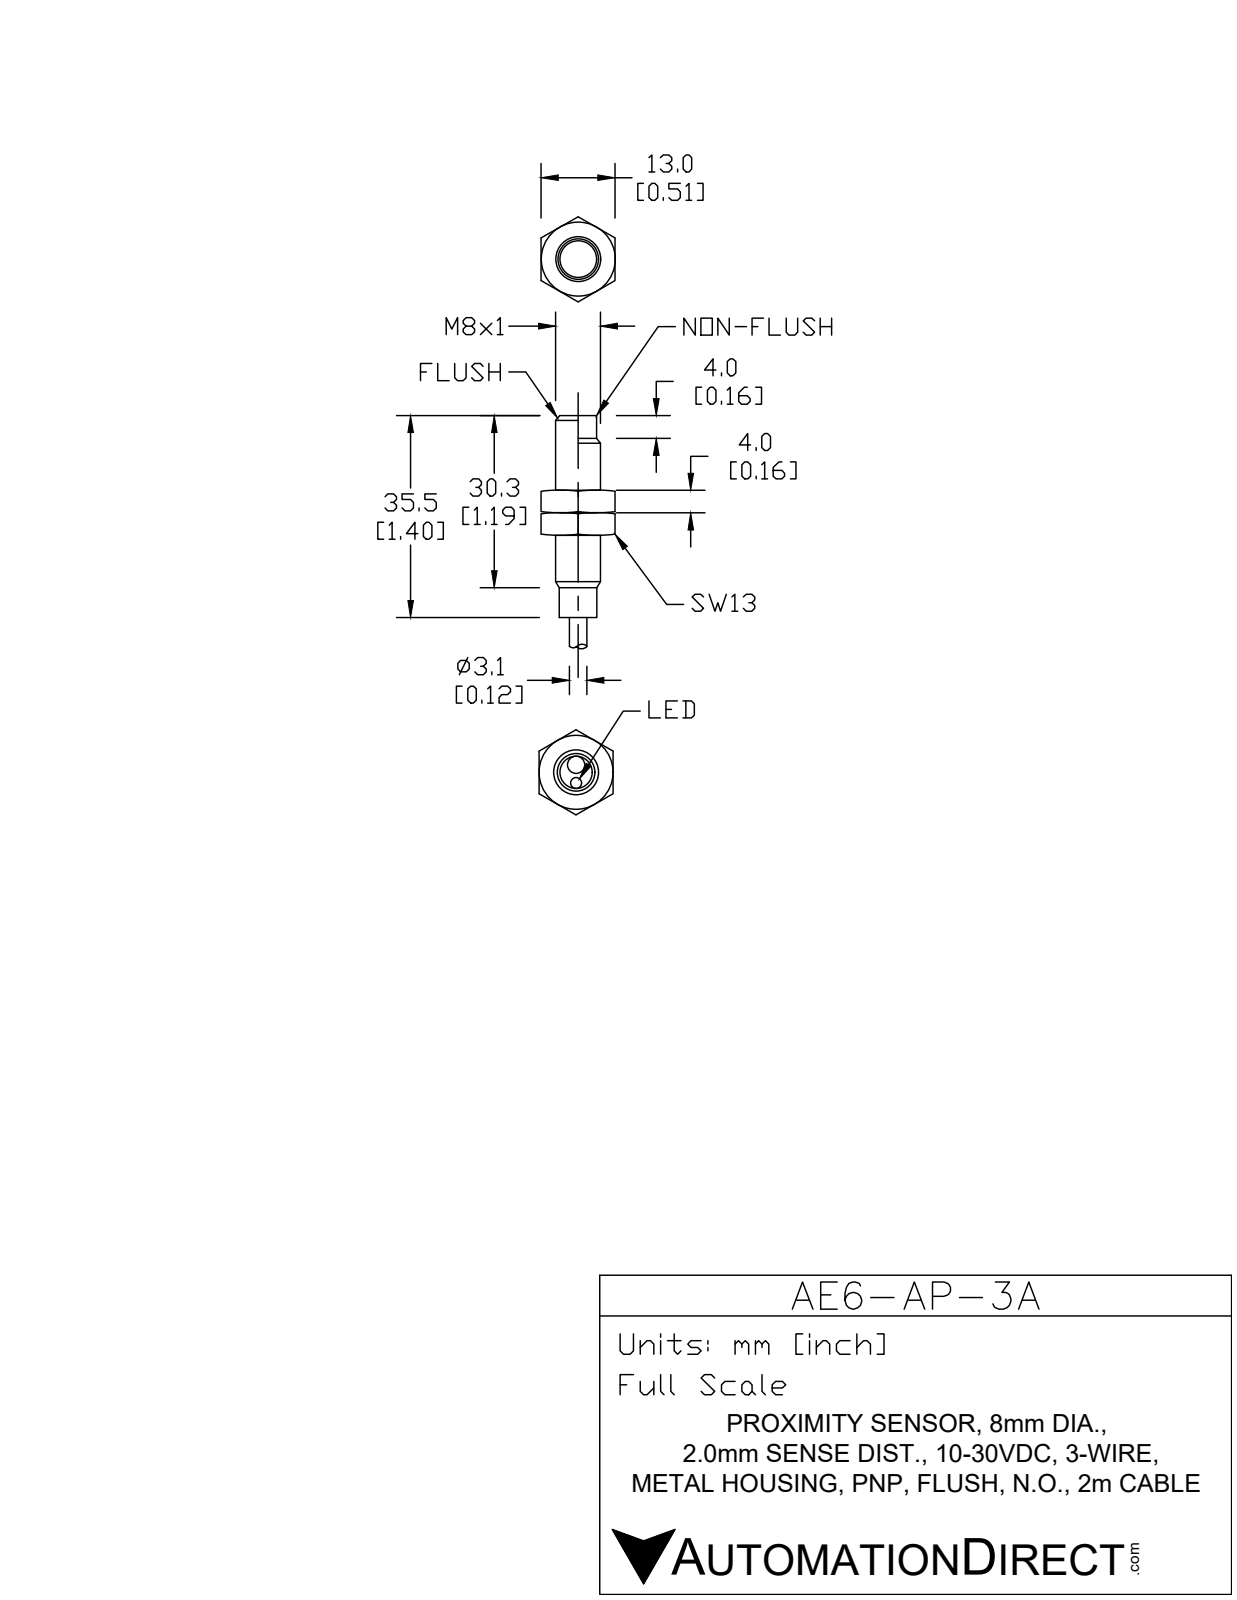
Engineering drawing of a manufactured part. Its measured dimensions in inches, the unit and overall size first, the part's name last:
Units: inches
Overall size (bounding box): 2.933 × 0.315 × 0.315
Round holes (diameter × count): ⌀0.122 ×1, ⌀0.228 ×1
Round bosses / shafts (diameter × count): ⌀0.315 ×1, ⌀0.256 ×1, ⌀0.254 ×1
Main face-to-face distances: 1.177, 1.189, 1.378, 1.366, 0.189, 0.02, 1.358, 1.346, 0.169, 2.933
Hole centre spacings: 0.045
Volume: 0.119 in³ · Surface area: 2.309 in²
Bodies: 4 solids, 30 faces (10 planar, 12 cylindrical, 8 other)
Part name (STEP PRODUCT): AE6-AP-3A
STEP written by: SolidWorks 2017 (AUTOMOTIVE_DESIGN)
